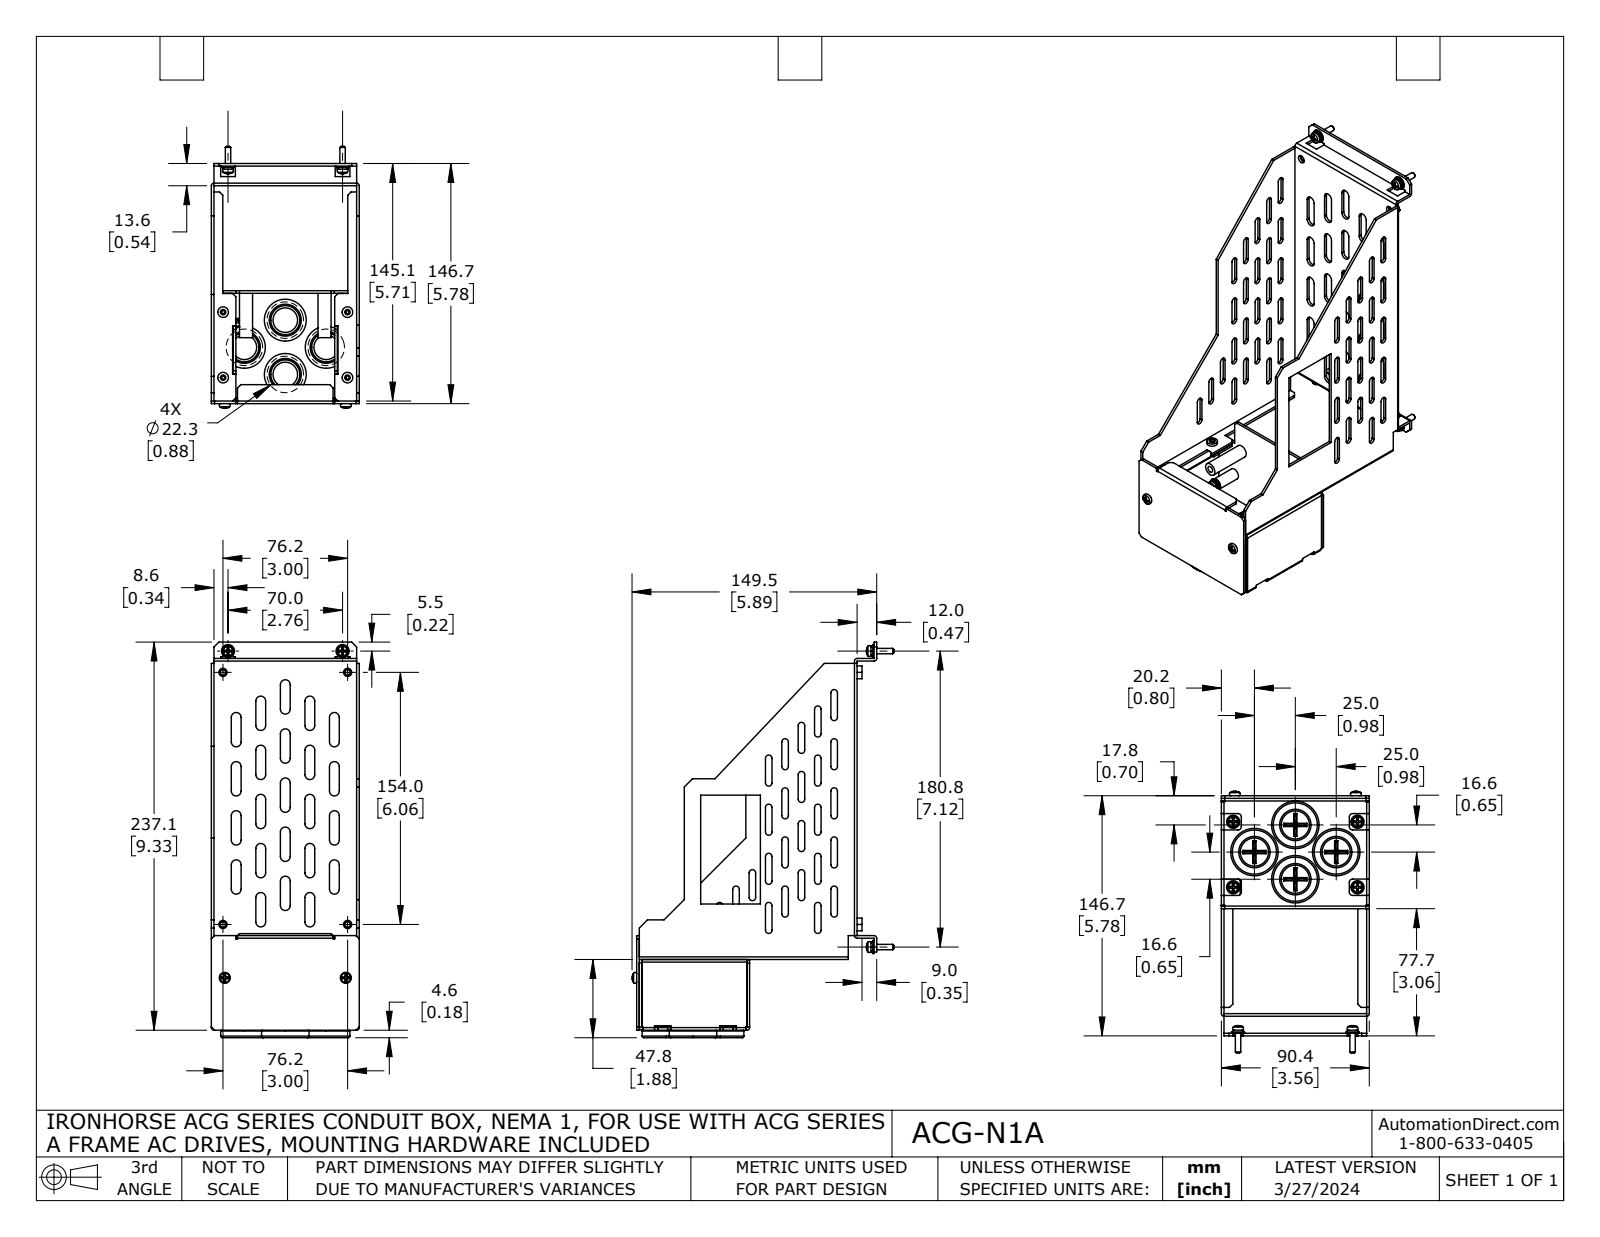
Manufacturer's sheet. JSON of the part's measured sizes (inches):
{"part_name": "ACG-N1A", "step_written_by": "SolidWorks 2021 (AUTOMOTIVE_DESIGN)", "units": "inches", "bodies": {"solids": 18, "faces": 1279, "planar": 672, "cylindrical": 468, "other": 139}, "overall_size": [9.516, 6.301, 3.559], "volume_in3": 7.532, "surface_area_in2": 248, "round_holes": [[0.13, 10], [0.197, 8], [0.677, 4], [0.878, 4], [1.024, 4], [0.157, 3], [0.169, 2]], "round_bosses_or_shafts": [[0.315, 11], [0.259, 9], [0.256, 6], [0.13, 5], [1.142, 4], [1.008, 4], [0.85, 4], [0.276, 1]], "partial_cylinders_radius": [[0.079, 58], [0.118, 46], [0.02, 24], [0.063, 17], [0.089, 4], [0.197, 3]], "face_to_face_distances": [0.063, 3.496, 3.559, 3.433, 5.24, 2.587, 2.654, 5.177, 2.591, 1.701], "hole_center_spacings": [1.181, 0.601, 0.891, 0.989, 1.116, 1.284, 1.498, 1.508]}
